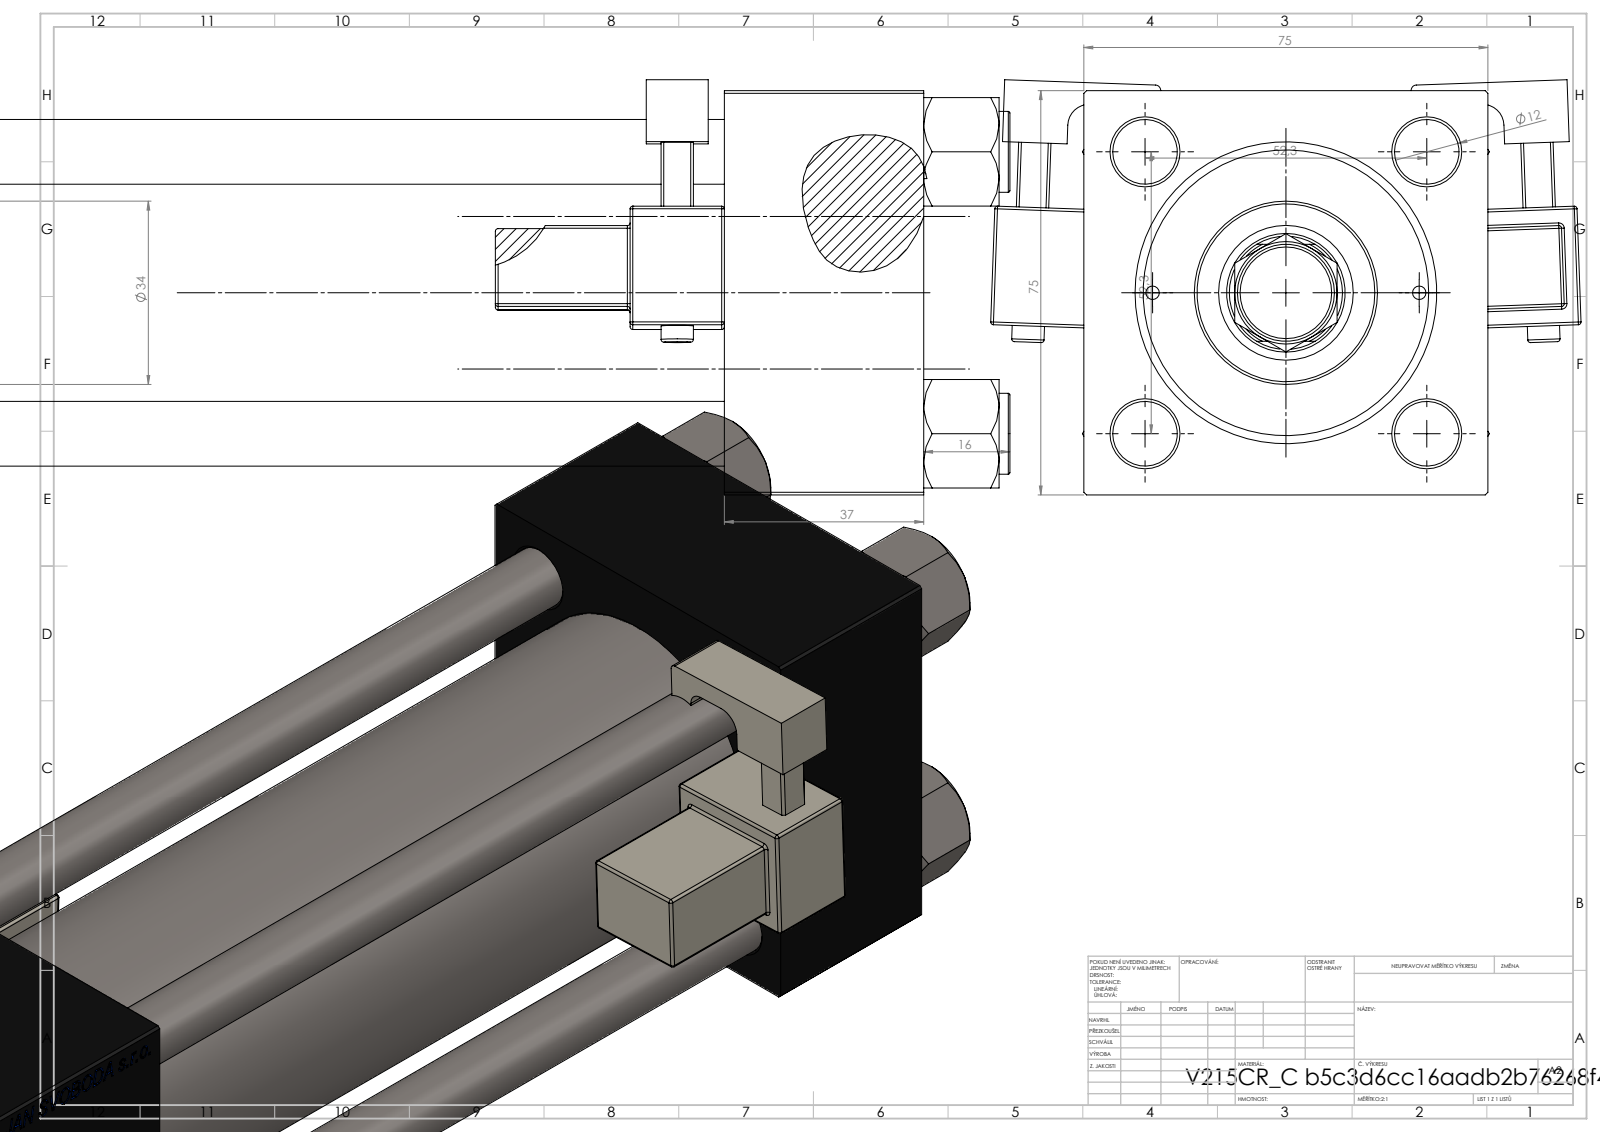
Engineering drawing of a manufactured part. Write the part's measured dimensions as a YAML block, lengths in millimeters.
part_name: "V215CR_C_TYCINKA; V215CR_VCP_C; V215_VC_A; V215CR_MSU (+3 more)"
step_written_by: "SolidWorks 2019 (CONFIG_CONTROL_DESIGN)"
units: millimeters
bodies: {solids: 14, faces: 1360, planar: 602, cylindrical: 154, other: 604}
overall_size: [333, 109.57, 77.03]
volume: 845993
surface_area: 220387
round_holes:
  - {diameter: 12, count: 4}
  - {diameter: 2.5, count: 2}
  - {diameter: 7, count: 2}
  - {diameter: 20.96, count: 2}
  - {diameter: 30, count: 2}
  - {diameter: 10.5, count: 1}
  - {diameter: 22, count: 1}
  - {diameter: 25, count: 1}
  - {diameter: 41, count: 1}
  - {diameter: 50, count: 1}
  - {diameter: 53, count: 1}
round_bosses_or_shafts:
  - {diameter: 15, count: 4}
  - {diameter: 6, count: 2}
  - {diameter: 56, count: 1}
  - {diameter: 34, count: 1}
  - {diameter: 18, count: 1}
  - {diameter: 11, count: 1}
partial_cylinders:
  - {radius: 0.5, count: 48}
  - {radius: 1, count: 2}
  - {radius: 2.5, count: 2}
  - {radius: 4, count: 2}
  - {radius: 10.5, count: 1}
face_to_face_distances: [75, 37, 259, 222, 200, 163, 59, 230.3, 193.3, 30.3]
hole_center_spacings: [26.19, 36.98, 52.3, 57.22, 24.75, 73.96, 49.5, 198.5]
